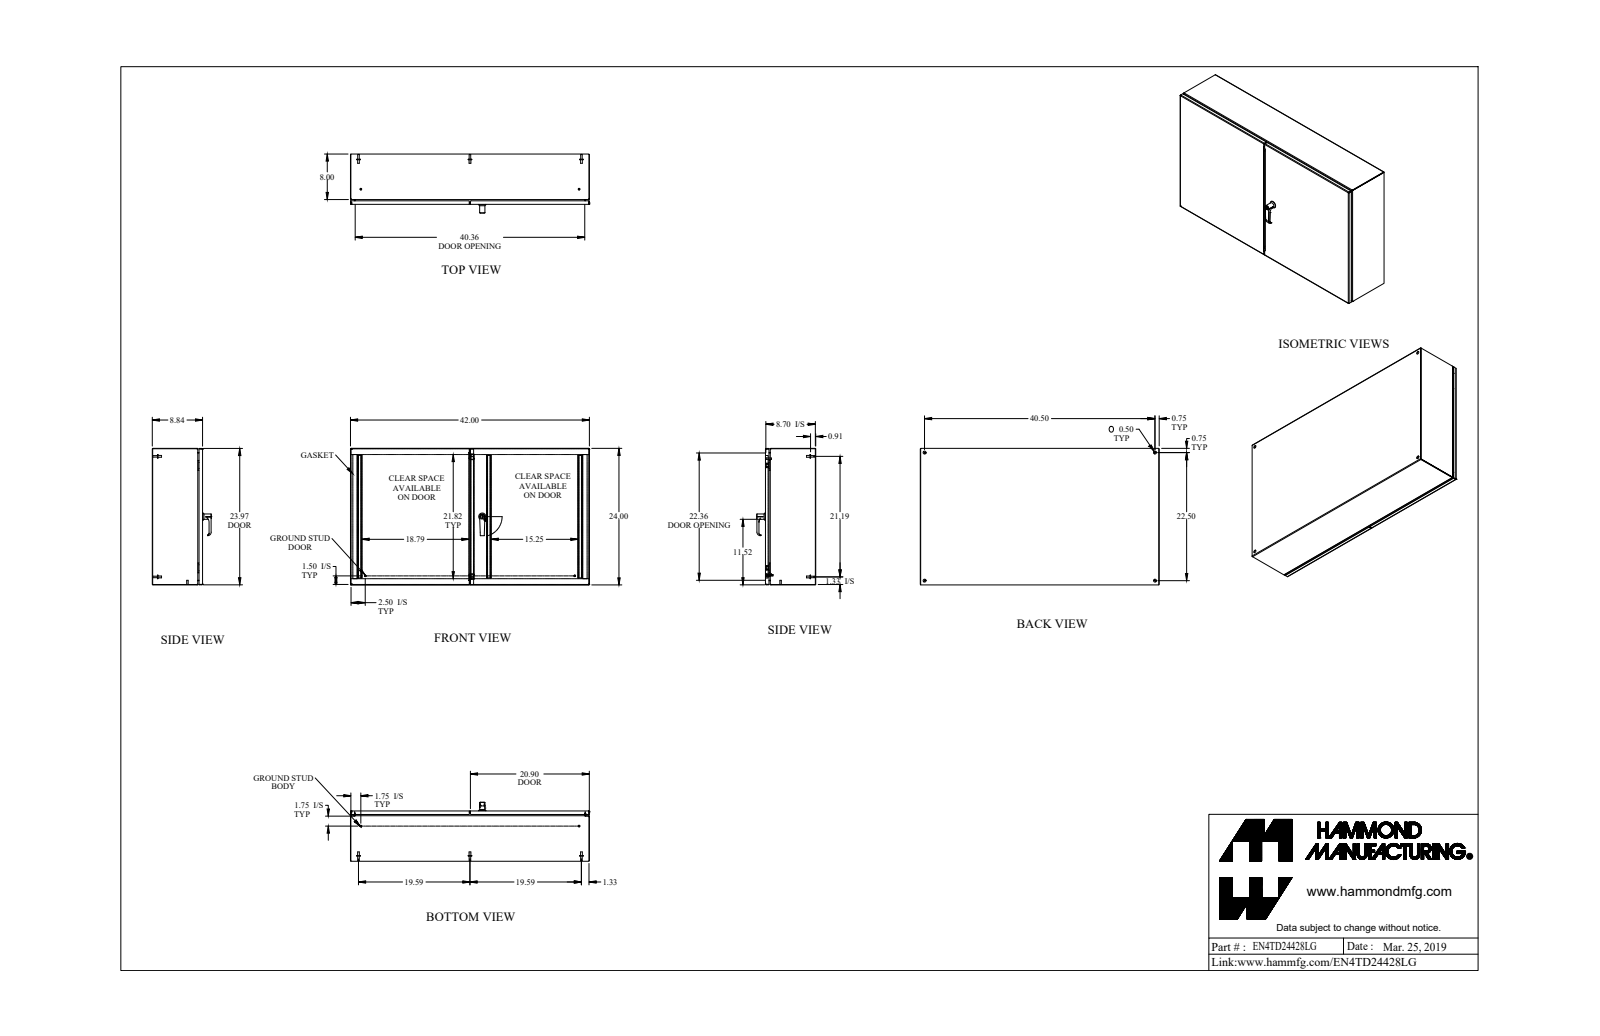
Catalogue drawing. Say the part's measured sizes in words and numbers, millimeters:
The part is named "EN4TD24428LG". Its 3-D file was written by "SolidWorks 2018 (AUTOMOTIVE_DESIGN)". It is 77 solids with 1935 faces: 883 planar, 714 cylindrical and 338 other. Overall it measures 1066.8 by 609.6 by 263.4 millimeters. Its volume is 4 716 000 cubic millimeters and its surface area 4 812 000 square millimeters. Round holes: 5 of diameter 5, 4 of diameter 4.5, 4 of diameter 6.7, 4 of diameter 12.7, 3 of diameter 6.1, 3 of diameter 6.1, 2 of diameter 4.4, 2 of diameter 6.4, 2 of diameter 6.5, 2 of diameter 6.6, 2 of diameter 8, 2 of diameter 10. Round bosses or shafts: 12 of diameter 6.4, 8 of diameter 8, 6 of diameter 15.9, 6 of diameter 6.9, 4 of diameter 13, 4 of diameter 9.5, 4 of diameter 7.1, 4 of diameter 4. Partial cylindrical surfaces (rounded edges, fillets, slot ends): 26 of radius 0.9, 26 of radius 2.7, 20 of radius 2.4, 18 of radius 1.1, 18 of radius 1.6, 18 of radius 2.1, 16 of radius 0.5, 15 of radius 0.4. The main face-to-face distances are 1.8, 222.8, 220.9, 224.6, 607.8, 1065, 605.9, 609.6, 1063.1, 1066.8. The hole center spacings are 20, 258.8, 540.9, 571.5, 578, 637.1, 1028.7, 1176.8.
